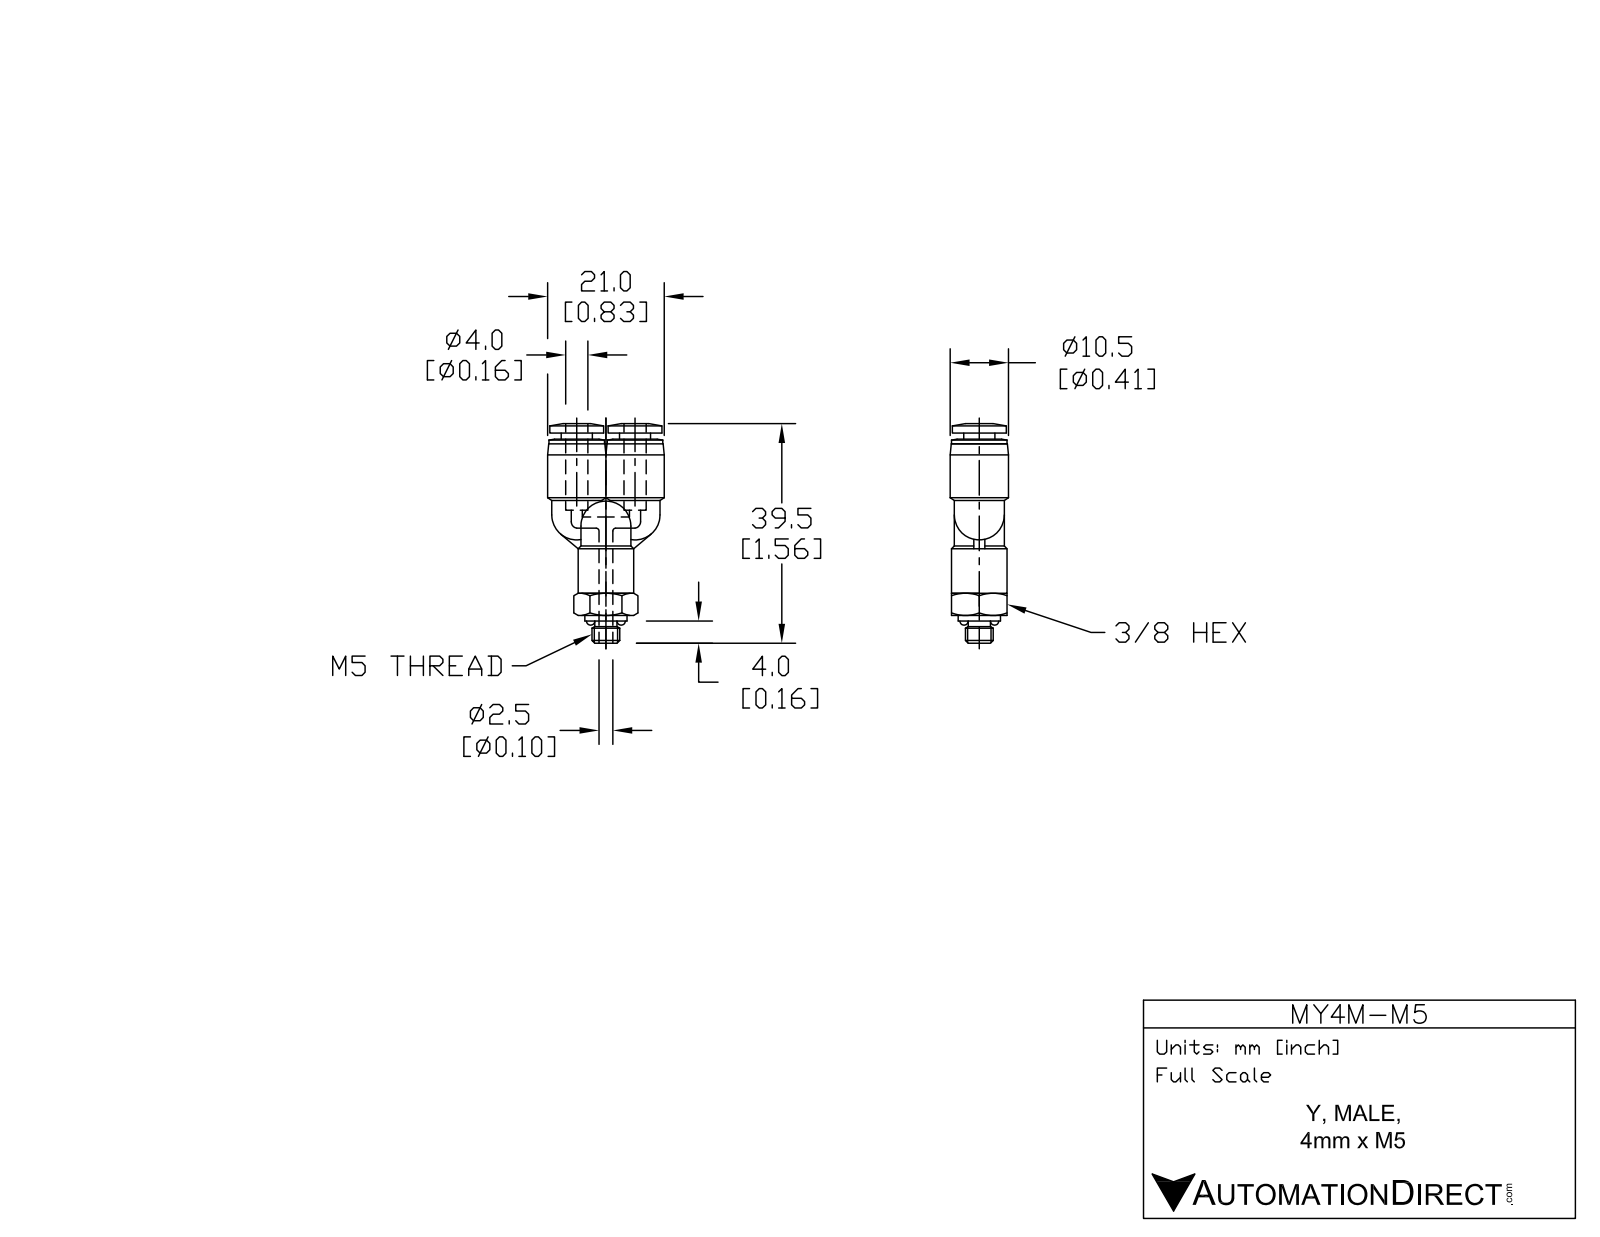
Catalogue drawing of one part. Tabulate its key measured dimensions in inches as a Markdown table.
| quantity | value |
| --- | --- |
| part name | MY4M-M5 |
| STEP written by | SolidWorks 2015 (AUTOMOTIVE_DESIGN) |
| units | inches |
| bodies | 2 solids, 127 faces (26 planar, 45 cylindrical, 56 other) |
| overall size | 1.549 × 0.827 × 0.413 |
| volume | 0.221 in³ |
| surface area | 4.56 in² |
| round holes (diameter × count) | 0.098 × 4, 0.169 × 2 |
| round bosses / shafts (diameter × count) | 0.394 × 3, 0.354 × 3, 0.413 × 2, 0.382 × 2, 0.22 × 2, 0.299 × 1, 0.197 × 1, 0.157 × 1 |
| main face-to-face distances | 0.394, 0.043, 1.242, 1.285, 0.157, 0.742, 0.5, 0.543, 0.236, 0.75 |
| hole center spacings | 0.207, 0.413 |
